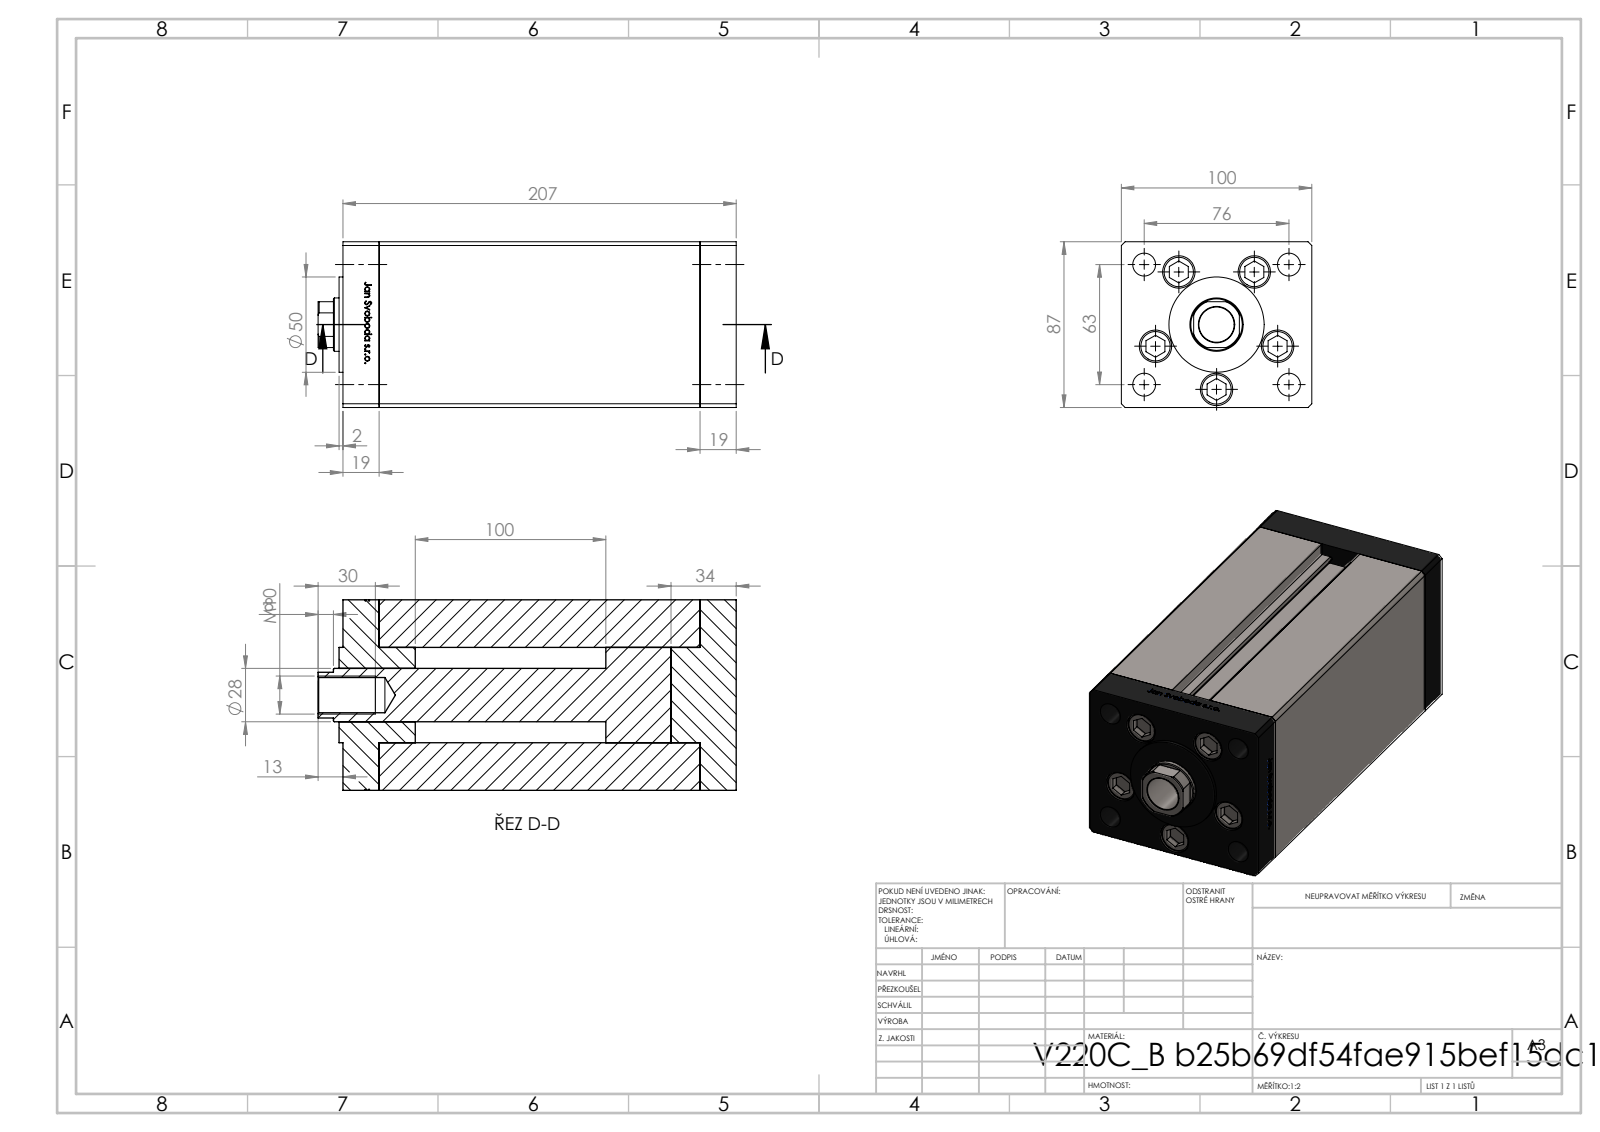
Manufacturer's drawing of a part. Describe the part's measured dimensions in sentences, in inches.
The part is named "V220C_B MIDDLE; V220C_VC_B; ALLEN BOLT; V220C_FRONT_B (+1 more)". Its 3-D file was written by "SolidWorks 2019 (CONFIG_CONTROL_DESIGN)". It is 14 solids with 1185 faces: 464 planar, 147 cylindrical and 574 other. Overall it measures 8.642 by 3.937 by 3.425 inches. Its volume is 96.11 cubic inches and its surface area 338.1 square inches. Round holes: 7 of diameter 0.531, 5 of diameter 0.669, 4 of diameter 0.472, 2 of diameter 0.079, 2 of diameter 0.518, 1 of diameter 0.728, 1 of diameter 1.102. Round bosses or shafts: 5 of diameter 0.315, 2 of diameter 0.669, 1 of diameter 1.969. Partial cylindrical surfaces (rounded edges, fillets, slot ends): 2 of radius 0.037, 1 of radius 0.531. The main face-to-face distances are 3.937, 3.425, 0.748, 6.634, 7.382, 1.348, 8.13, 0.6, 6.033, 6.781. The hole center spacings are 1.339, 0.732, 1.561, 1.943, 2.281, 0.828, 1.499, 1.546.
